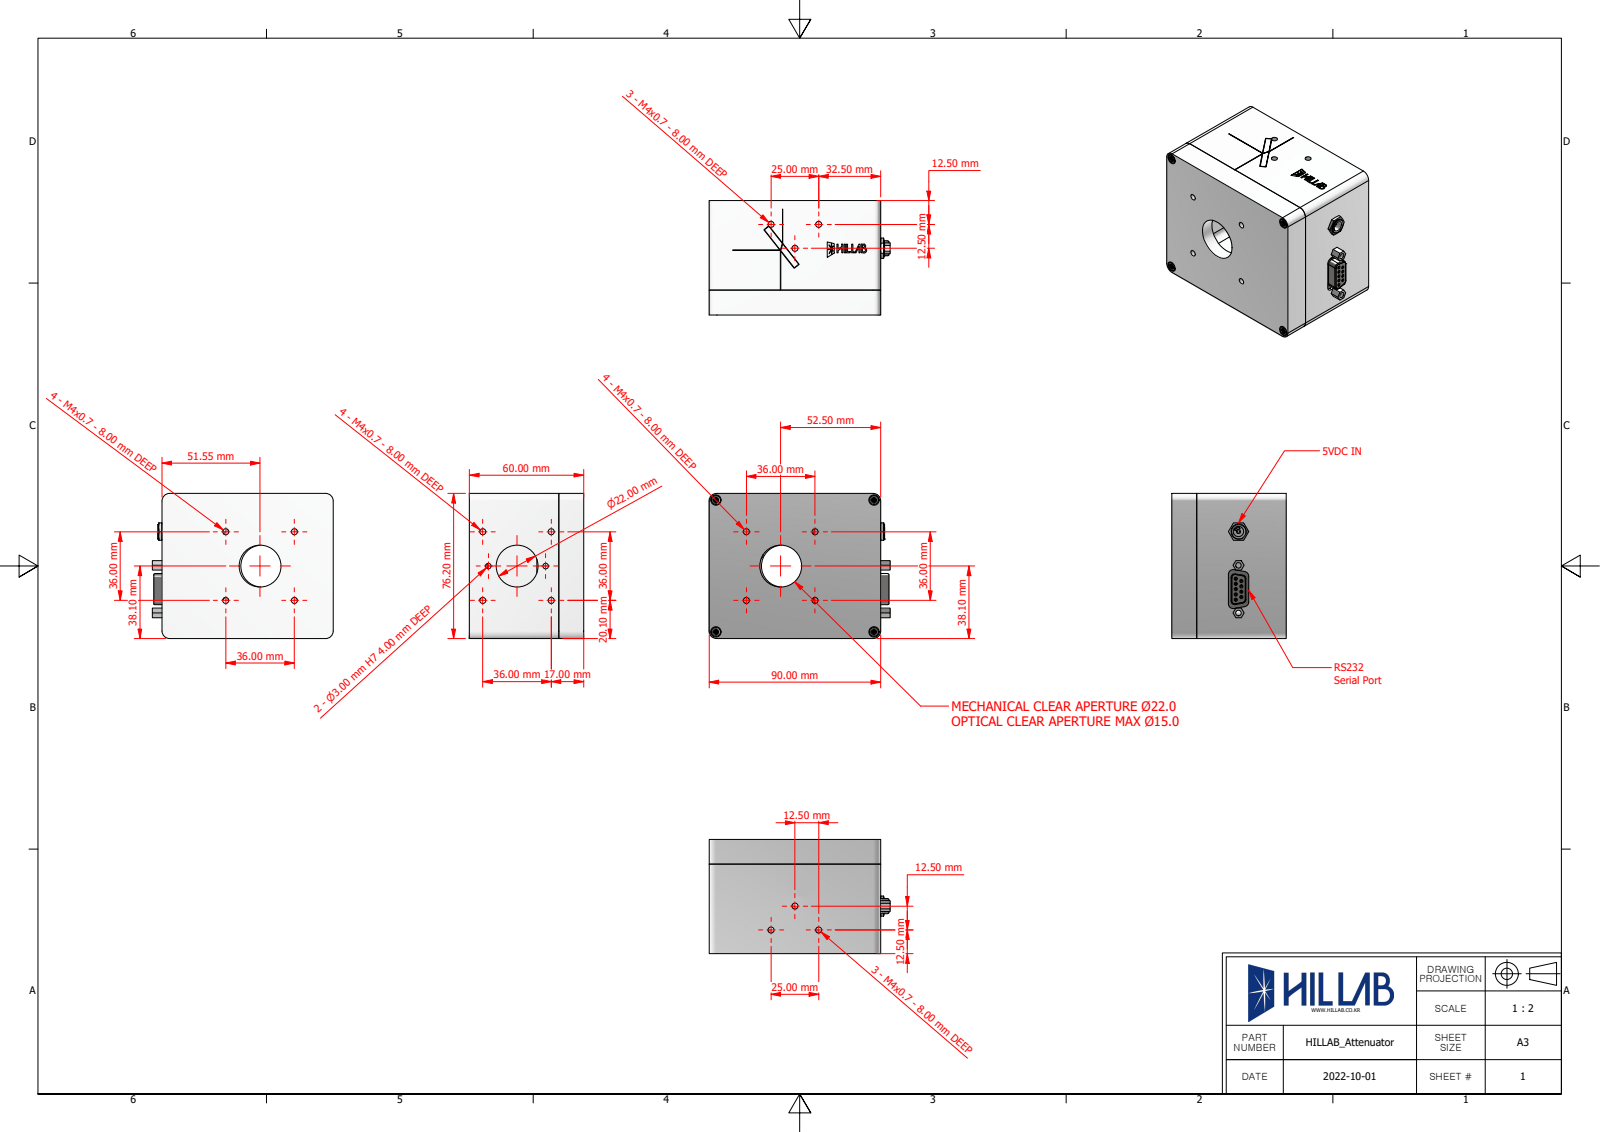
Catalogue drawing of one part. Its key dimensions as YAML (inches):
part_name: "ATT; B01_front cover; B02_frame; 09672XX47XX_100630886MOD000A (+4 more)"
step_written_by: "Autodesk Inventor 2025 (AUTOMOTIVE_DESIGN)"
units: inches
bodies: {solids: 17, faces: 1140, planar: 529, cylindrical: 351, other: 260}
overall_size: [3.74, 3, 2.362]
volume: 11.14
surface_area: 109.5
round_holes:
  - {diameter: 0.128, count: 15}
  - {diameter: 0.031, count: 9}
  - {diameter: 0.035, count: 9}
  - {diameter: 0.039, count: 9}
  - {diameter: 0.079, count: 8}
  - {diameter: 0.097, count: 8}
  - {diameter: 0.118, count: 5}
  - {diameter: 0.114, count: 4}
  - {diameter: 0.866, count: 3}
  - {diameter: 0.12, count: 2}
  - {diameter: 0.126, count: 2}
  - {diameter: 0.102, count: 1}
round_bosses_or_shafts:
  - {diameter: 0.047, count: 9}
  - {diameter: 0.185, count: 4}
  - {diameter: 0.098, count: 4}
  - {diameter: 0.087, count: 4}
  - {diameter: 0.419, count: 1}
  - {diameter: 0.315, count: 1}
  - {diameter: 0.285, count: 1}
  - {diameter: 0.263, count: 1}
partial_cylinders:
  - {radius: 0.079, count: 34}
  - {radius: 0.02, count: 20}
  - {radius: 0.016, count: 18}
  - {radius: 0.157, count: 18}
  - {radius: 0.039, count: 16}
  - {radius: 0.063, count: 12}
  - {radius: 0.011, count: 9}
  - {radius: 0.018, count: 9}
face_to_face_distances: [0.276, 2.362, 2.087, 3, 0.37, 1.717, 1.992, 3.543, 0.177, 2.823]
hole_center_spacings: [1.002, 1.417, 1.948, 0.109, 2.004, 0.037, 0.218, 0.124]
